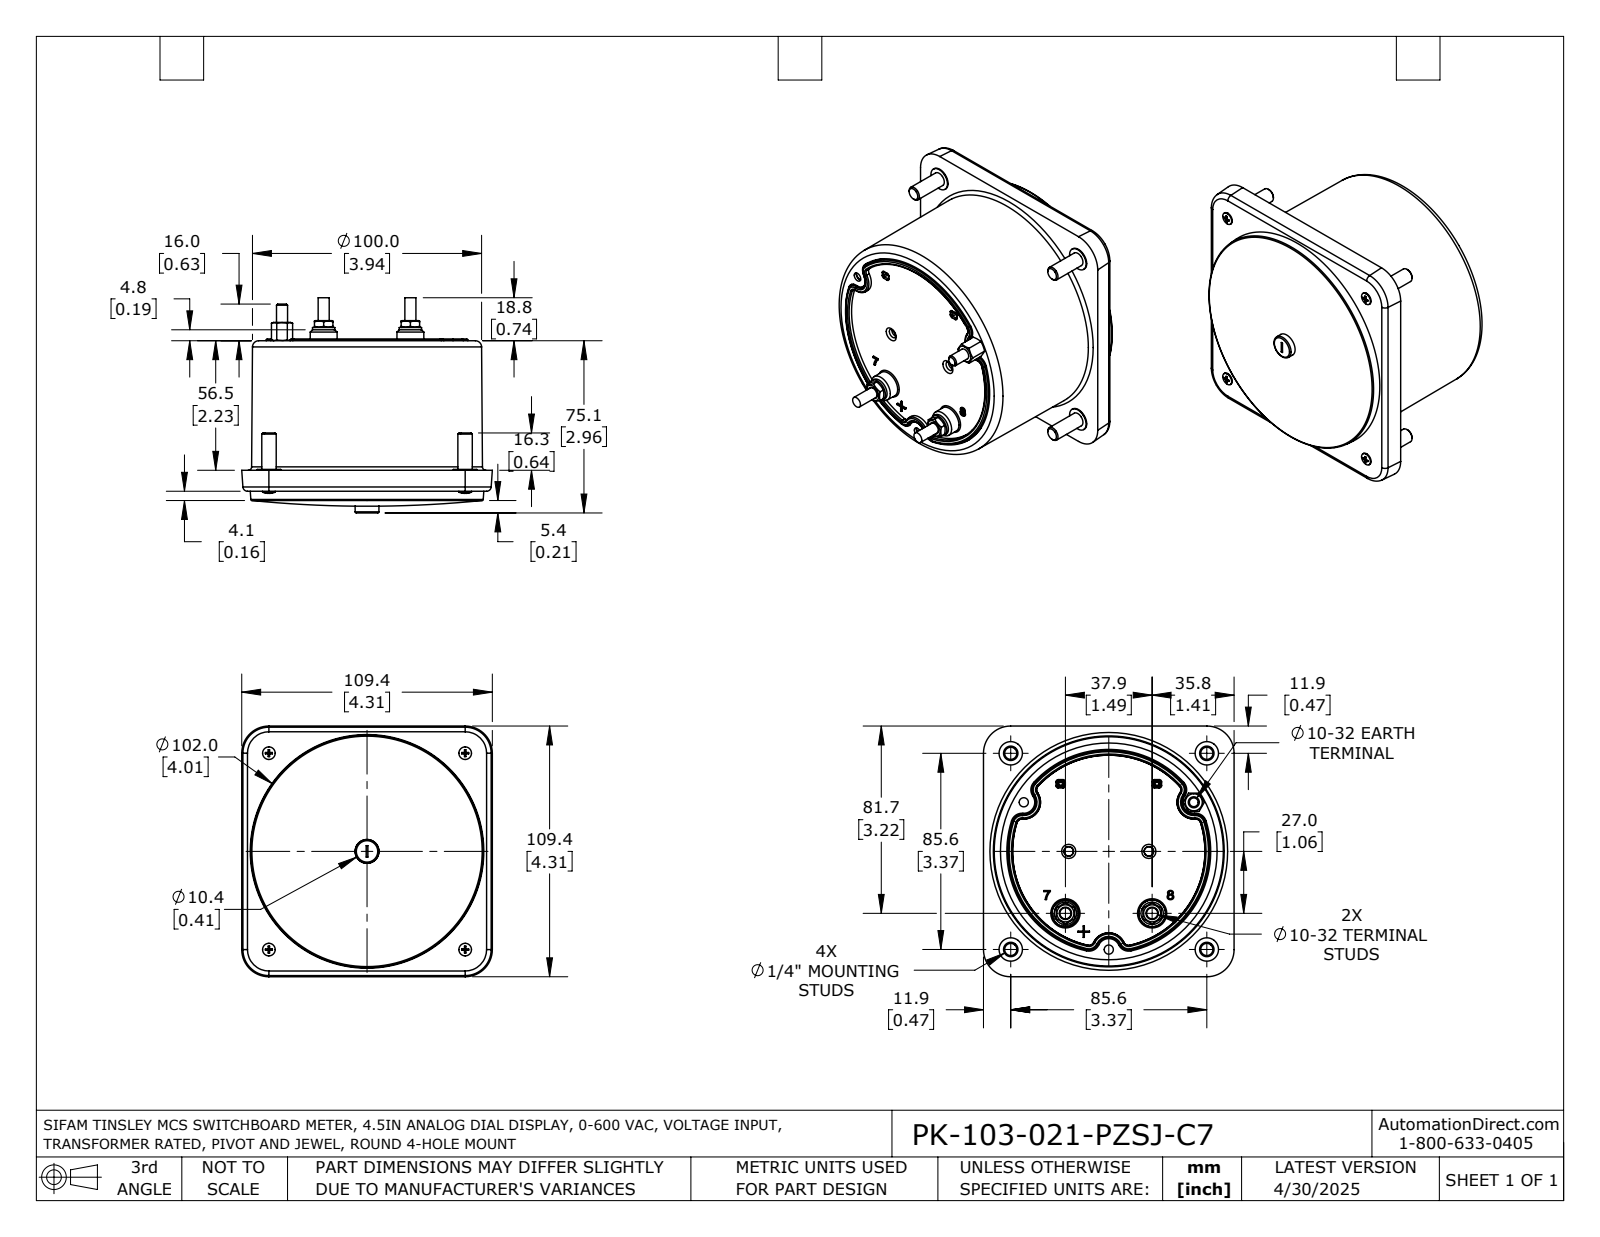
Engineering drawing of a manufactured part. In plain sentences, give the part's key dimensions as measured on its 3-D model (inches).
The part is named "PK-103-021-PZSJ-C7". Its 3-D file was written by "SolidWorks 2021 (AUTOMOTIVE_DESIGN)". It is 1 solid with 609 faces: 167 planar, 141 cylindrical and 301 other. Overall it measures 4.307 by 4.307 by 3.697 inches. Its volume is 36.28 cubic inches and its surface area 82.21 square inches. Round holes: 4 of diameter 0.094, 4 of diameter 0.138, 4 of diameter 0.315, 3 of diameter 0.157, 2 of diameter 0.209. Round bosses or shafts: 4 of diameter 0.402, 4 of diameter 0.248, 4 of diameter 0.217, 4 of diameter 0.114, 3 of diameter 0.19, 2 of diameter 0.384, 1 of diameter 0.146. Partial cylindrical surfaces (rounded edges, fillets, slot ends): 24 of radius 0.02, 9 of radius 0.189, 4 of radius 0.079, 1 of radius 1.752. The main face-to-face distances are 2.177, 2.537, 0.36, 0.048, 2.225, 2.585, 0.489, 2.715, 2.667, 0.129. The hole center spacings are 3.372, 3.37, 3.374, 3.378, 3.38, 4.769, 0.971, 1.126.
